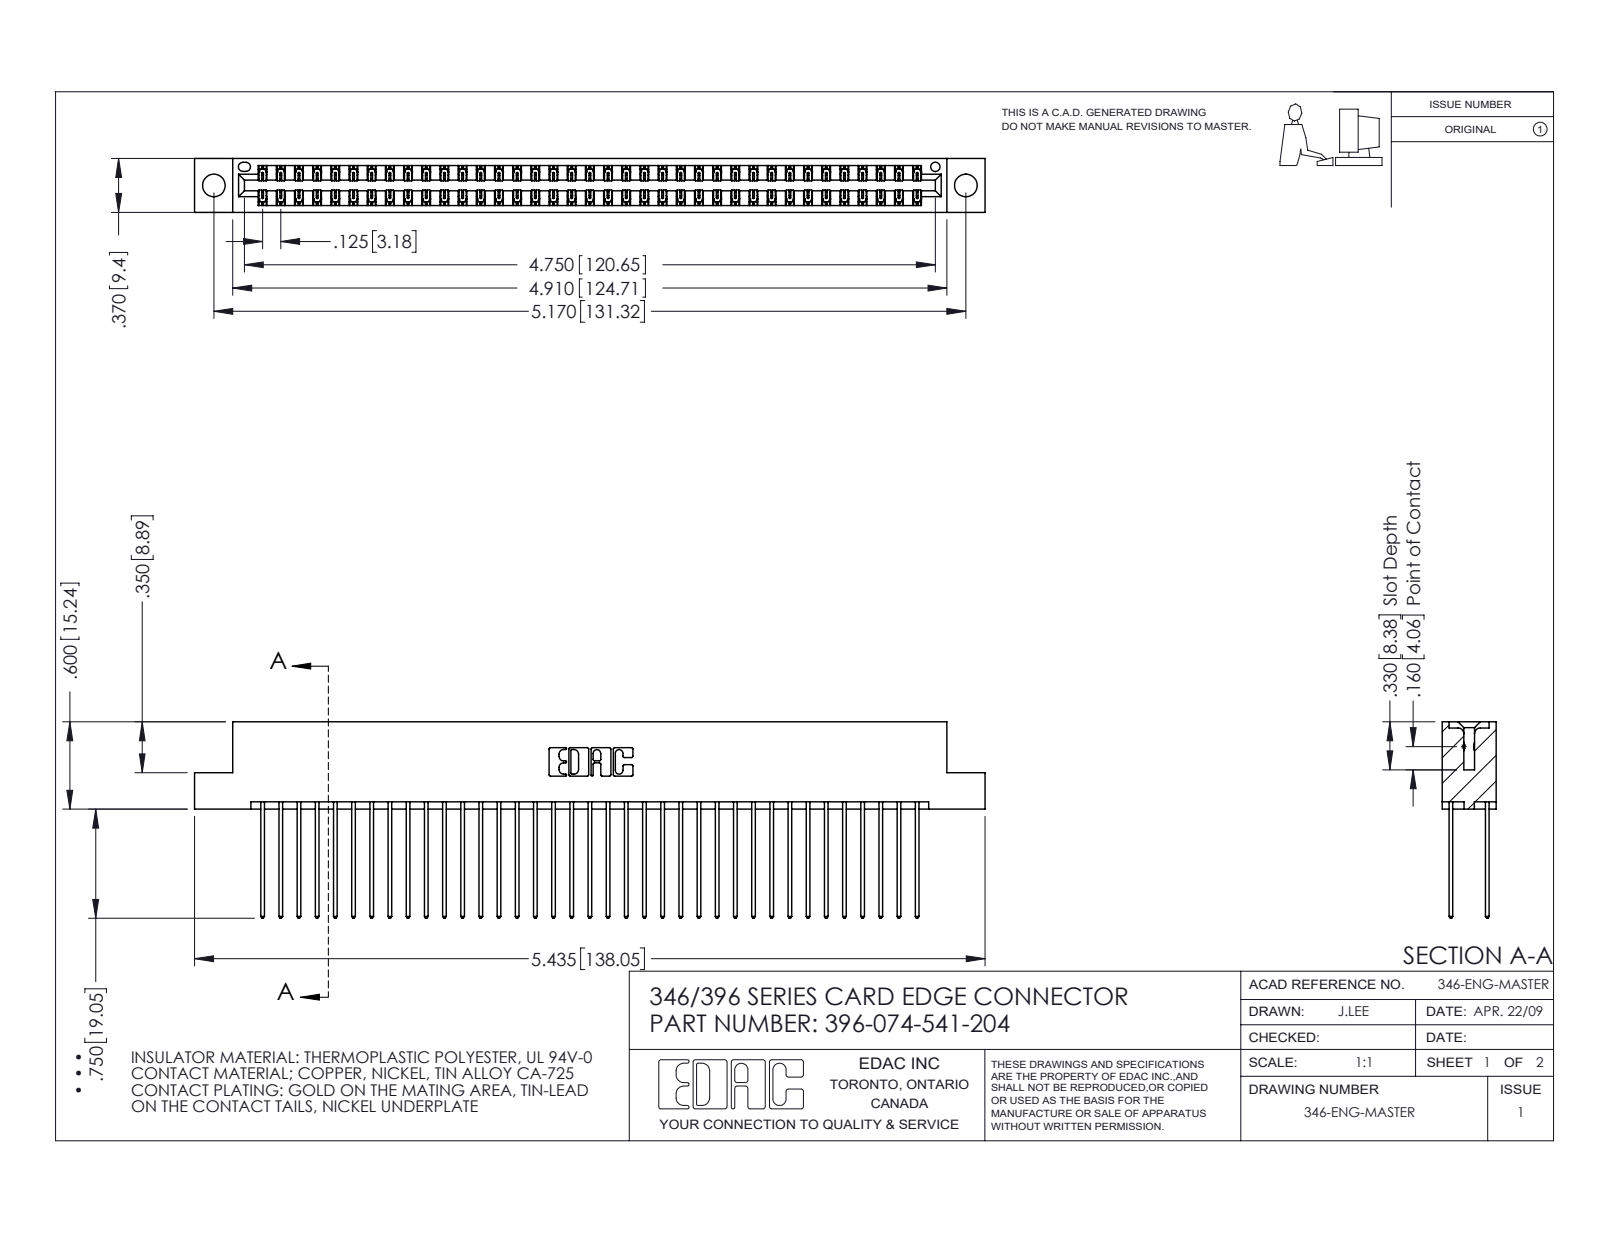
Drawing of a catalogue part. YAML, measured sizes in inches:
part_name: "345-292-001_345-293-141; 346 Part_Flush Mounting Lugs - 0.156 Dia-TH; 396-074-541-204"
step_written_by: "SolidWorks 2016 (CONFIG_CONTROL_DESIGN)"
units: inches
bodies: {solids: 75, faces: 3970, planar: 2666, cylindrical: 1304, other: 0}
overall_size: [5.435, 1.35, 0.37]
volume: 0.84
surface_area: 32.06
round_holes:
  - {diameter: 0.156, count: 2}
  - {diameter: 0.064, count: 1}
partial_cylinders:
  - {radius: 0.006, count: 111}
  - {radius: 0.01, count: 74}
  - {radius: 0.01, count: 22}
  - {radius: 0.007, count: 6}
  - {radius: 0.031, count: 6}
  - {radius: 0.026, count: 3}
  - {radius: 0.014, count: 2}
  - {radius: 0.022, count: 2}
face_to_face_distances: [0.048, 0.322, 0.25, 0.072, 0.298, 0.025, 0.37, 0.275, 0.225, 0.148]
hole_center_spacings: [0.246, 4.961, 5.17]
